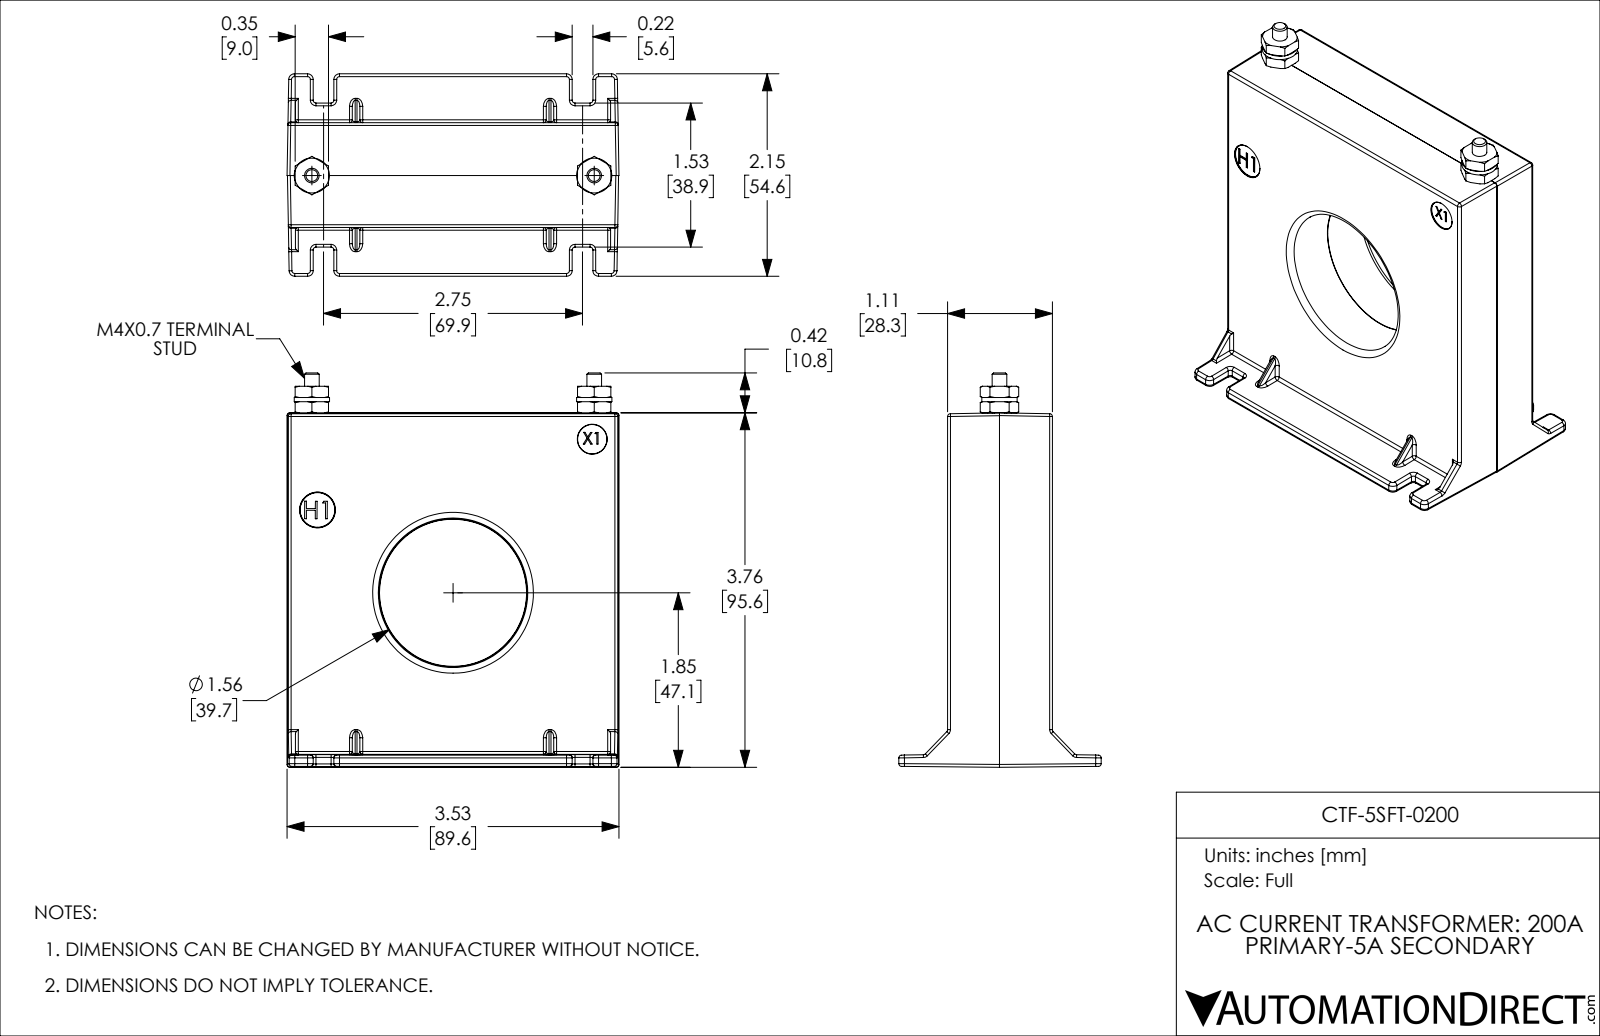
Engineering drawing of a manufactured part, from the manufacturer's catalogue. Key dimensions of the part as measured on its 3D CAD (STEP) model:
Part name (STEP PRODUCT): CTF-5SFT-0200
STEP written by: SolidWorks 2018 (AUTOMOTIVE_DESIGN)
Units: inches
Bodies: 10 solids, 437 faces (134 planar, 156 cylindrical, 147 other)
Overall size (bounding box): 4.188 × 3.527 × 2.15
Volume: 13.01 in³ · Surface area: 75.78 in²
Round holes (diameter × count): ⌀0.155 ×2, ⌀0.165 ×2, ⌀0.155 ×1, ⌀0.312 ×1, ⌀0.375 ×1
Round bosses / shafts (diameter × count): ⌀0.375 ×2
Partial cylindrical surfaces — rounded edges, fillets, slot ends (radius × count): R0.03 ×92, R0.06 ×12
Main face-to-face distances: 0.562, 1.113, 0.551, 3.523, 3.616, 0.163, 0.045, 0.118, 0.519, 1.632
Hole centre spacings: 3, 3.015
